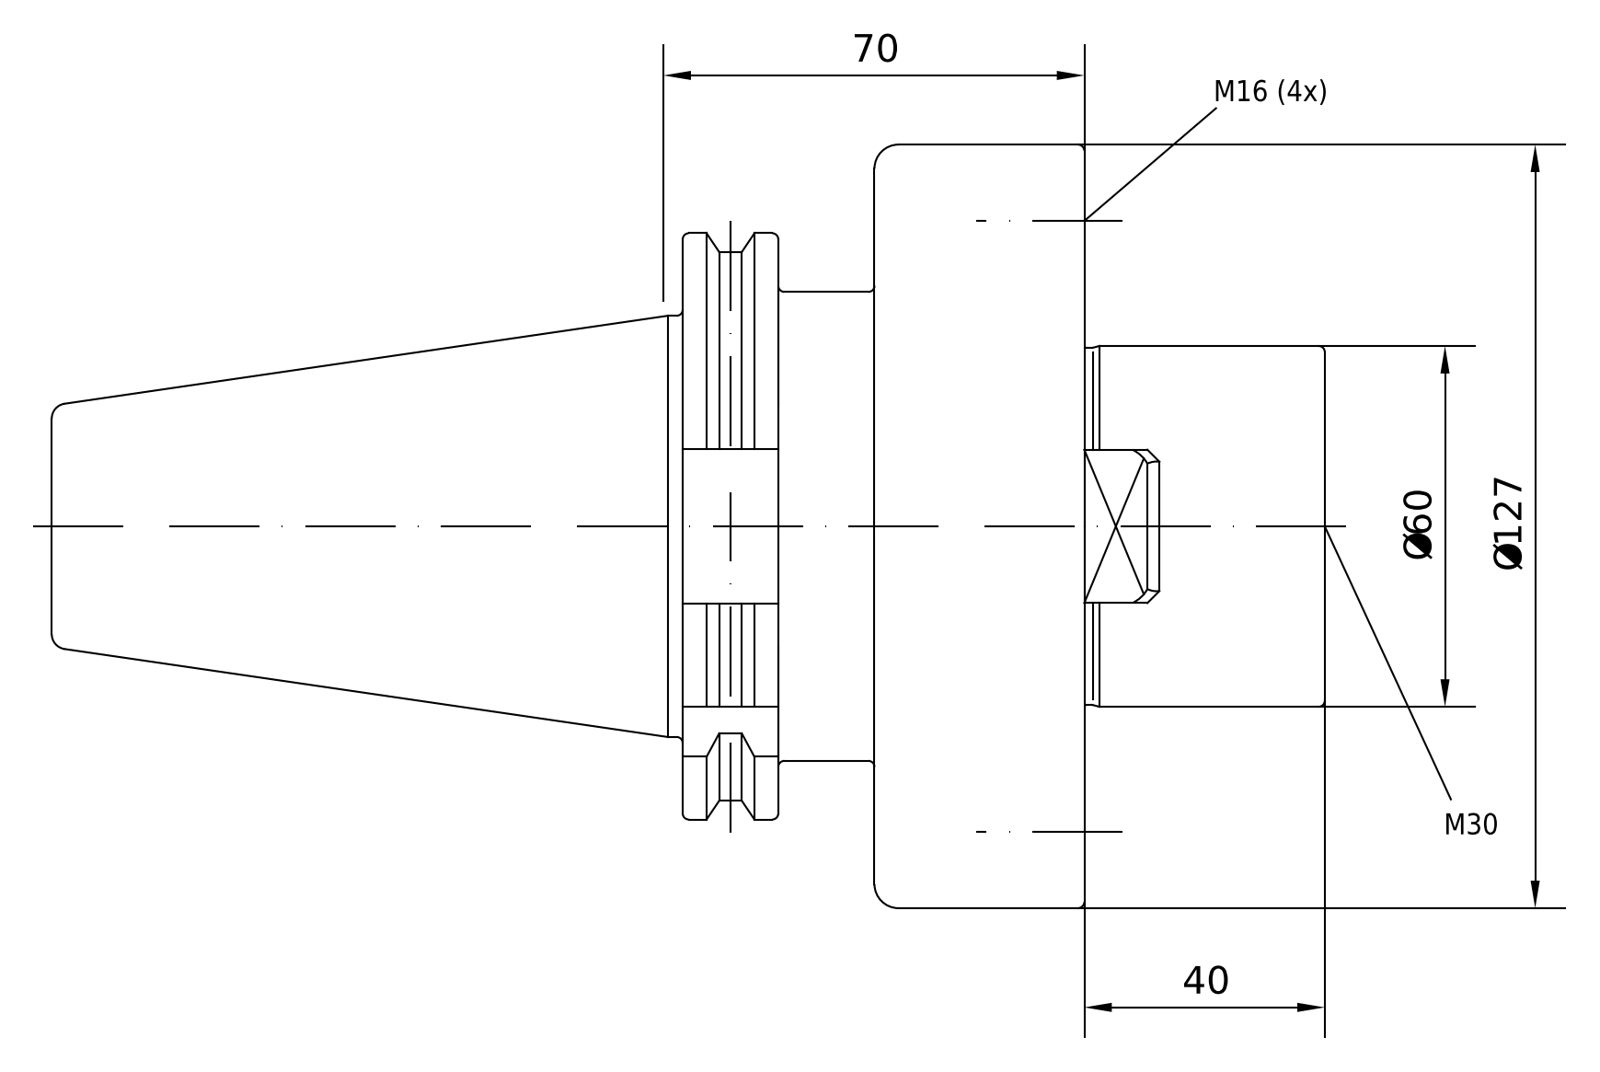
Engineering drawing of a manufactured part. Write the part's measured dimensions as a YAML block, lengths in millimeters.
part_name: "50-350-60"
step_written_by: "PRO/ENGINEER BY PARAMETRIC TECHNOLOGY CORPORATION, 2010430 (CONFIG_CONTROL_DESIGN)"
units: millimeters
bodies: {solids: 1, faces: 146, planar: 38, cylindrical: 46, other: 62}
overall_size: [211.6, 127, 127]
volume: 923386
surface_area: 106899
round_holes:
  - {diameter: 14, count: 4}
  - {diameter: 16, count: 4}
  - {diameter: 20.75, count: 1}
  - {diameter: 25.01, count: 1}
  - {diameter: 25.7, count: 1}
  - {diameter: 26.5, count: 1}
  - {diameter: 30, count: 1}
round_bosses_or_shafts:
  - {diameter: 127, count: 1}
  - {diameter: 91, count: 1}
  - {diameter: 69.15, count: 1}
  - {diameter: 60, count: 1}
  - {diameter: 24.01, count: 1}
partial_cylinders:
  - {radius: 1.75, count: 1}
  - {radius: 39, count: 1}
  - {radius: 48.74, count: 1}
face_to_face_distances: [34.95, 31.85, 66.8, 106.8, 74.95, 40, 15.85, 16, 50.95, 90.95]
hole_center_spacings: [50.8, 71.84, 101.6]
